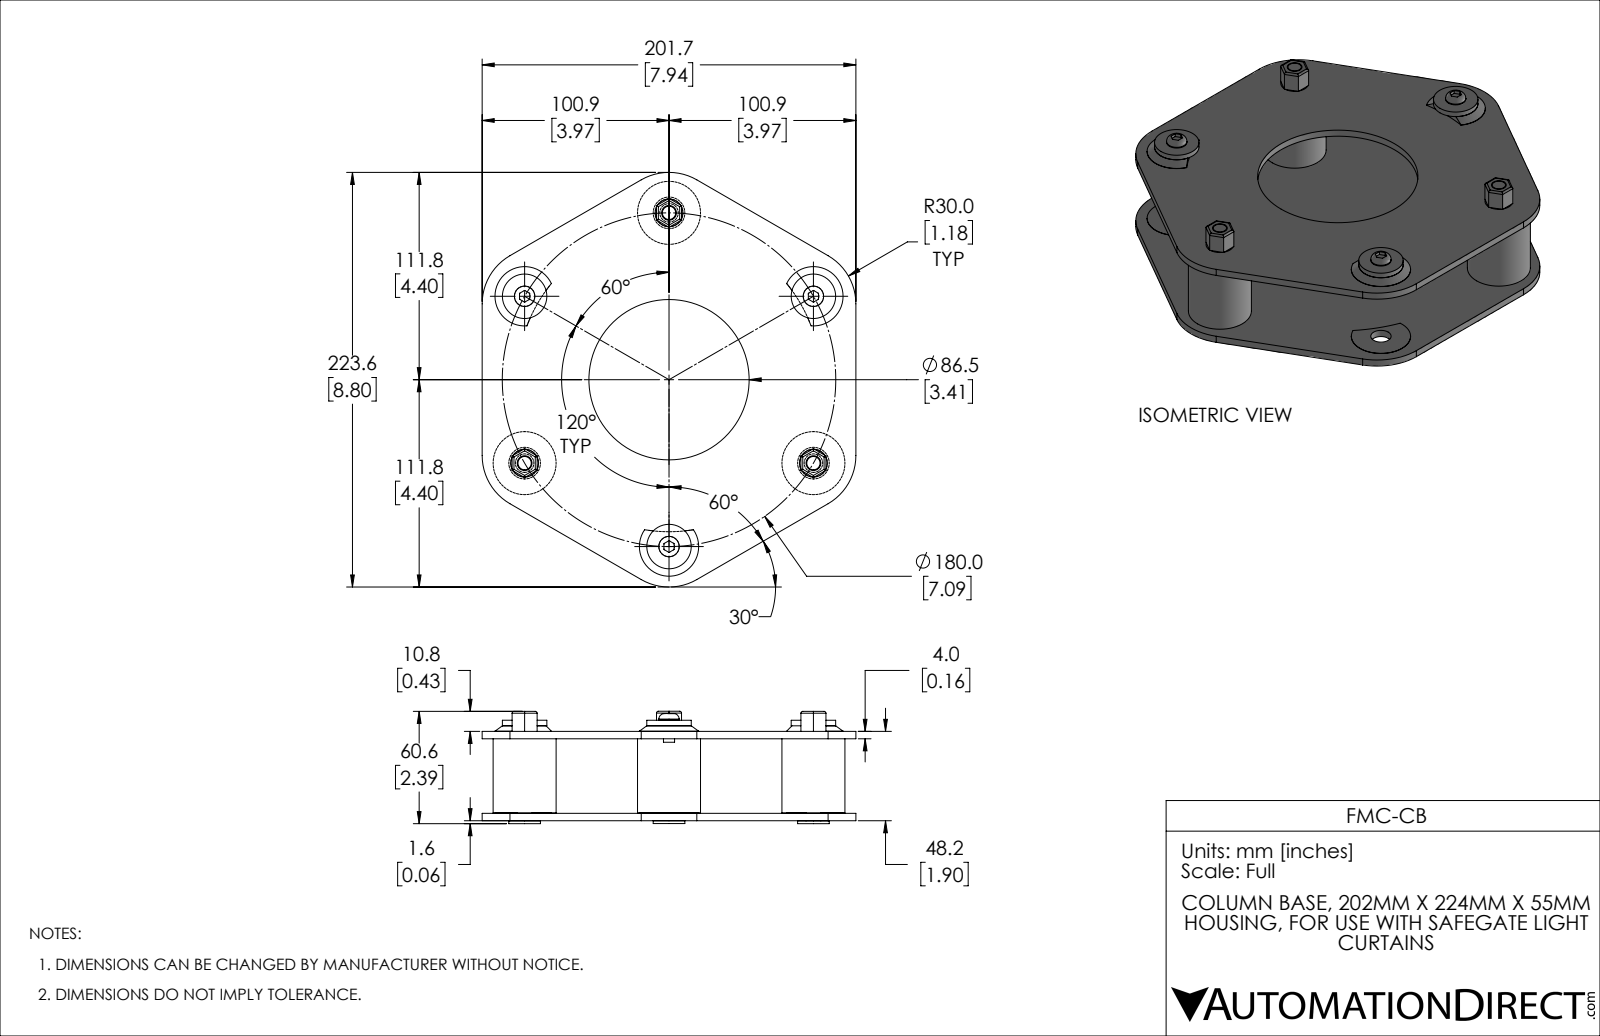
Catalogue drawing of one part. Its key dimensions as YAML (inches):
part_name: "FMC-CB"
step_written_by: "SolidWorks 2019 (AUTOMOTIVE_DESIGN)"
units: inches
bodies: {solids: 20, faces: 185, planar: 97, cylindrical: 76, other: 12}
overall_size: [8.805, 7.942, 2.388]
volume: 23.53
surface_area: 259.1
round_holes:
  - {diameter: 0.236, count: 3}
  - {diameter: 0.283, count: 3}
  - {diameter: 0.394, count: 3}
  - {diameter: 0.433, count: 3}
  - {diameter: 3.406, count: 1}
round_bosses_or_shafts:
  - {diameter: 1.339, count: 3}
  - {diameter: 0.945, count: 3}
  - {diameter: 0.673, count: 3}
  - {diameter: 0.433, count: 3}
  - {diameter: 0.315, count: 3}
partial_cylinders:
  - {radius: 0.039, count: 18}
  - {radius: 1.181, count: 6}
  - {radius: 0.63, count: 3}
  - {radius: 3.228, count: 1}
face_to_face_distances: [0.157, 1.74, 1.583, 1.898, 0.118, 1.575, 2.016, 1.858, 0.276, 7.942]
hole_center_spacings: [3.543, 6.137, 7.087]
